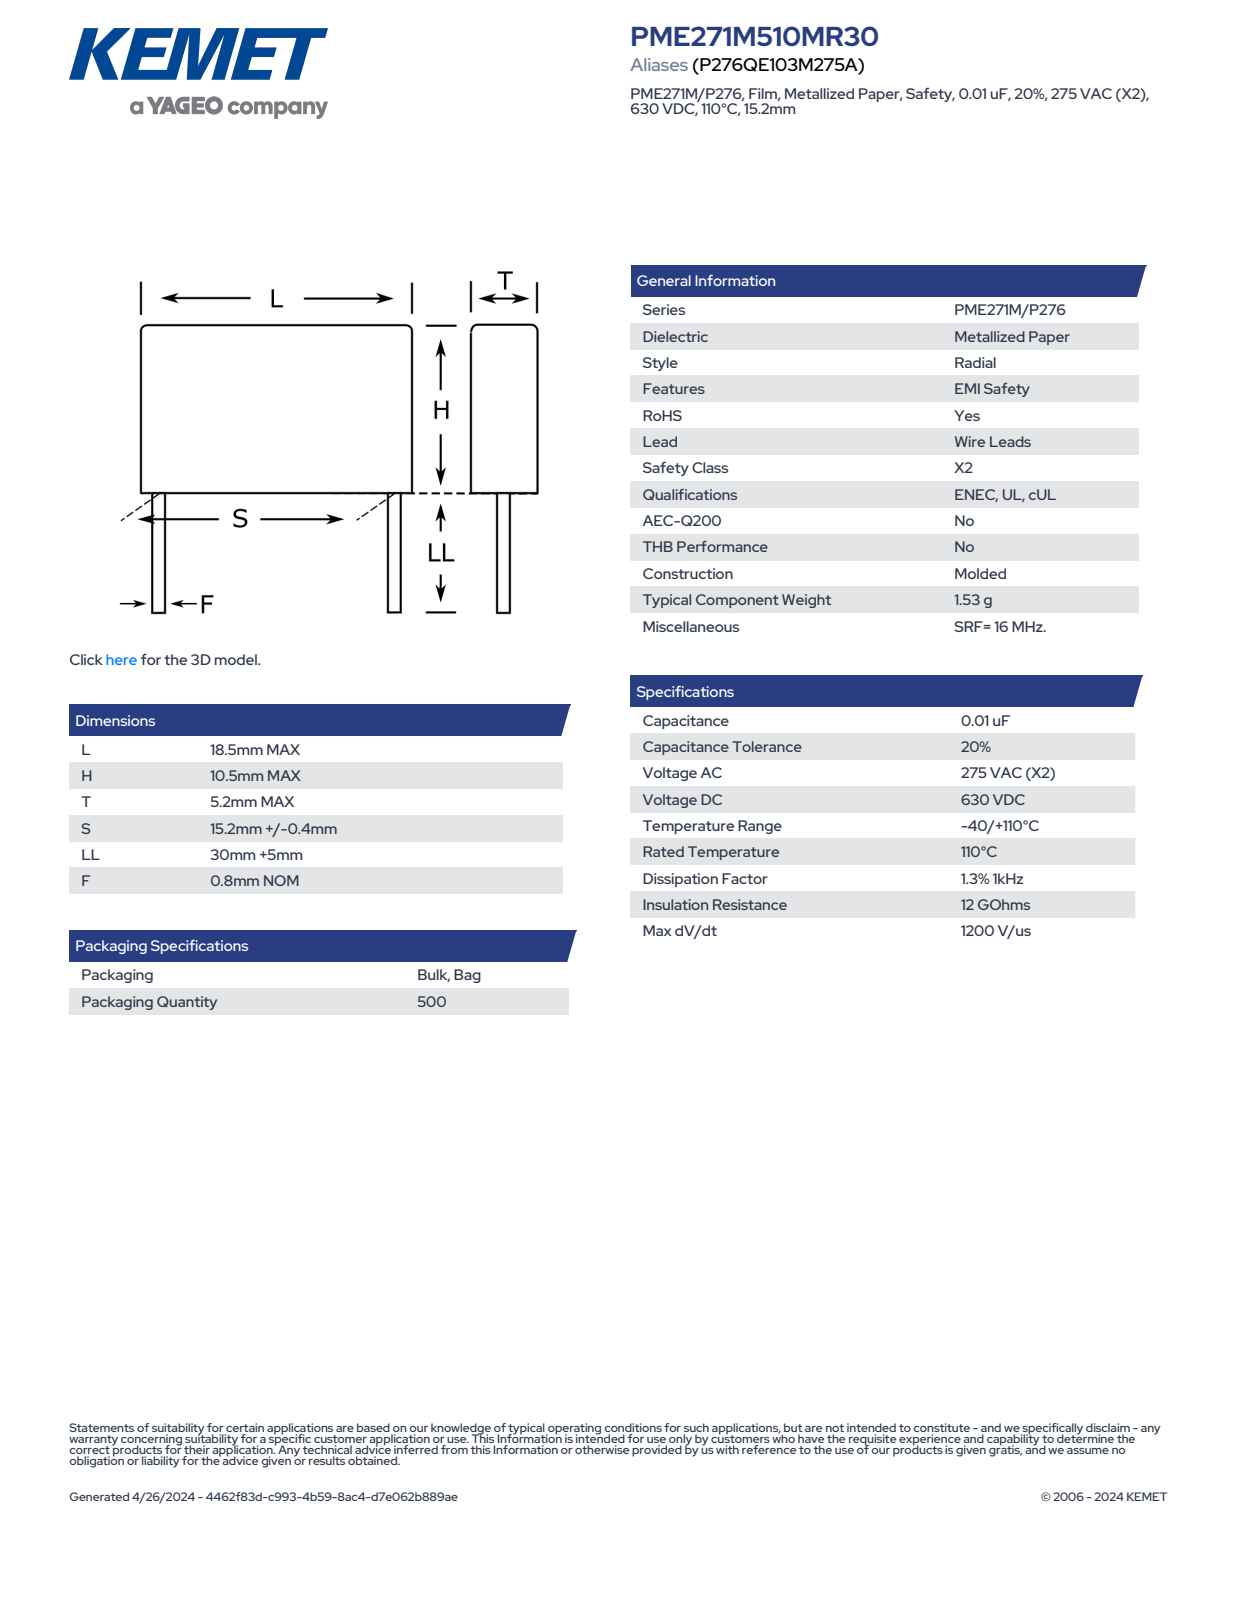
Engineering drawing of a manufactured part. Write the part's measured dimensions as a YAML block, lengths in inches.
part_name: "CFR_MOLDED_18.5X10.5X5.2_L18.5H10.5T5.2S15.2LL35F0.8"
step_written_by: "SolidWorks 2014 (AUTOMOTIVE_DESIGN)"
units: inches
bodies: {solids: 4, faces: 73, planar: 65, cylindrical: 8, other: 0}
overall_size: [1.791, 0.728, 0.205]
volume: 0.064
surface_area: 1.35
round_bosses_or_shafts:
  - {diameter: 0.031, count: 2}
partial_cylinders:
  - {radius: 0.02, count: 4}
face_to_face_distances: [0.205, 0.413, 0.728, 1.378, 1.791, 1.617, 0.239, 0.175, 1.551, 0.173]
